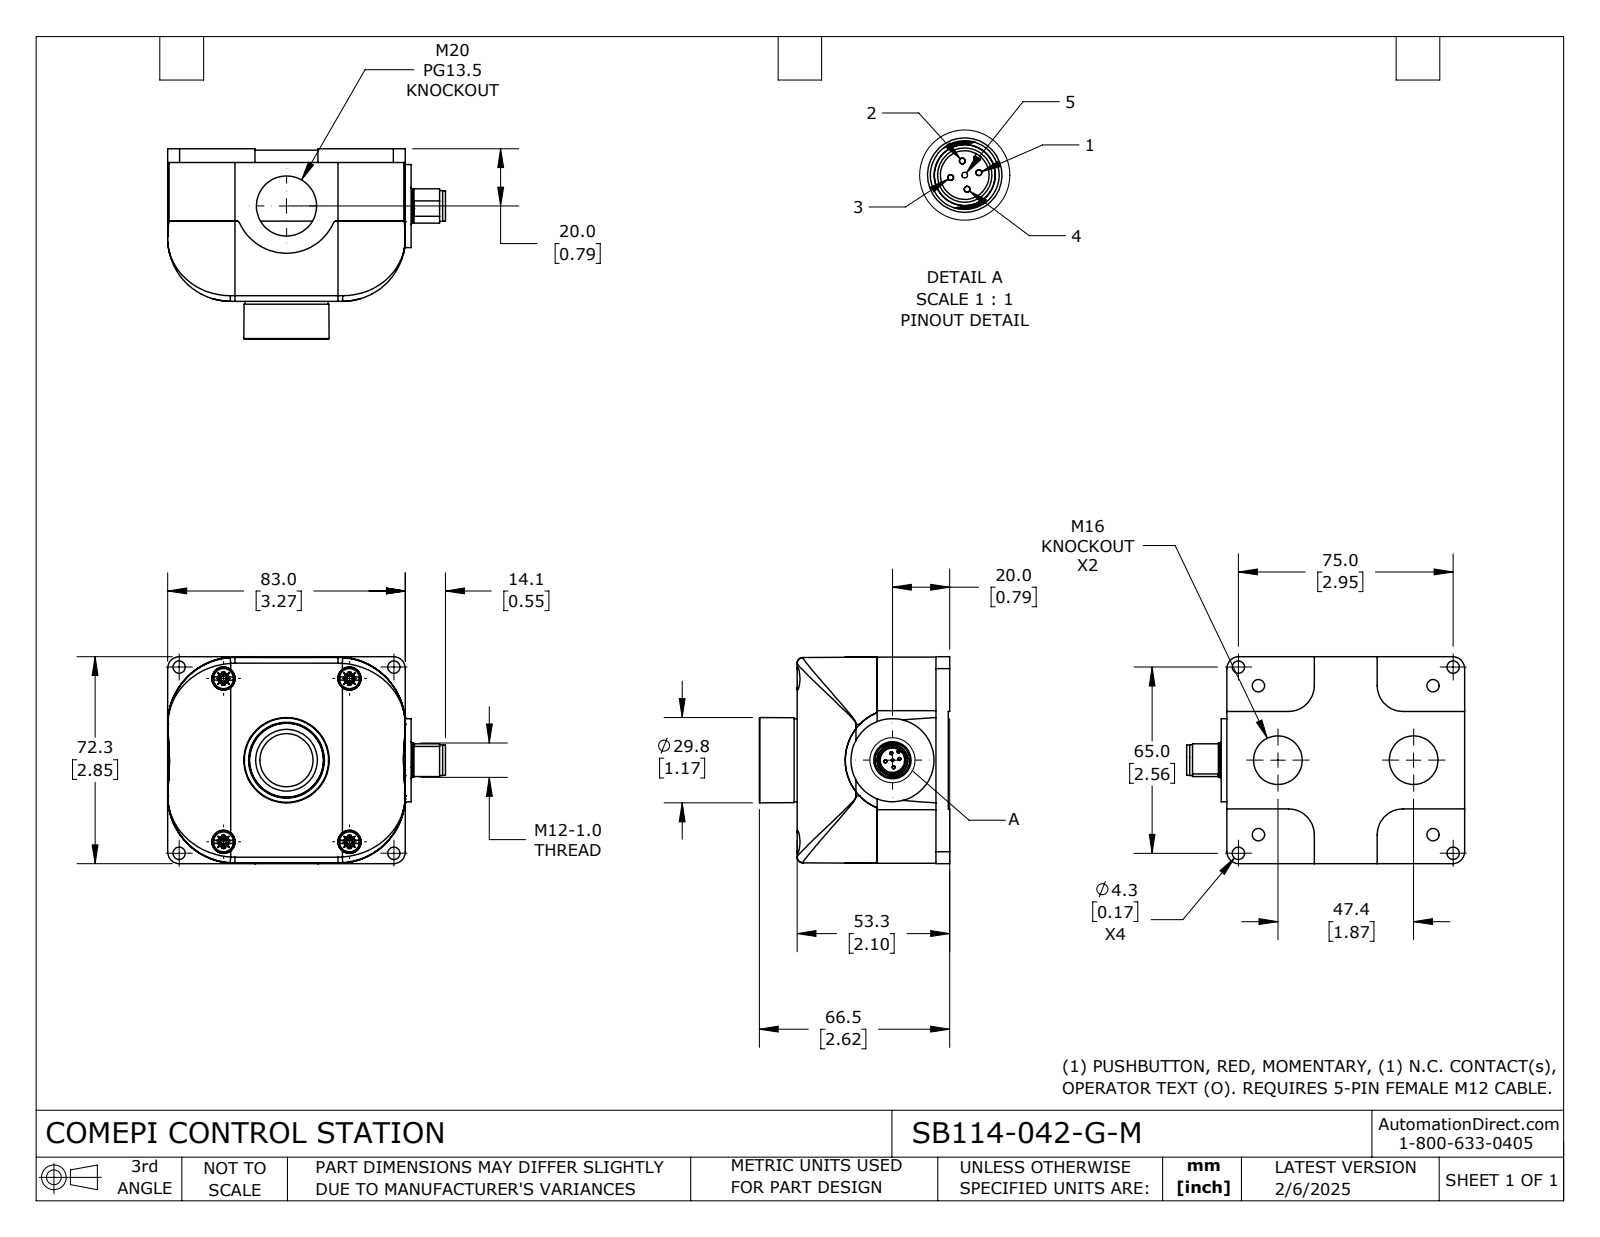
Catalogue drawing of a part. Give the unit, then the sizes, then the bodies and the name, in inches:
Units: inches
Overall size (bounding box): 3.821 × 2.846 × 2.618
Round holes (diameter × count): ⌀0.169 ×8, ⌀0.04 ×4, ⌀0.067 ×4, ⌀0.087 ×4, ⌀0.323 ×4, ⌀0.669 ×2, ⌀0.827 ×2, ⌀0.335 ×1, ⌀0.531 ×1, ⌀0.713 ×1, ⌀0.854 ×1
Round bosses / shafts (diameter × count): ⌀0.039 ×5, ⌀0.276 ×4, ⌀0.085 ×4, ⌀0.065 ×4, ⌀1.142 ×2, ⌀0.024 ×2, ⌀1.039 ×1, ⌀1.016 ×1
Partial cylindrical surfaces — rounded edges, fillets, slot ends (radius × count): R0.02 ×5, R0.035 ×4, R0.079 ×4, R0.354 ×4, R0.38 ×4, R0.925 ×4, R0.008 ×2, R0.01 ×2
Main face-to-face distances: 0.976, 0.098, 0.878, 2.079, 1.98, 1.102, 0.118, 2.098, 0.02, 0.996
Hole centre spacings: 0.376, 1.058, 1.39, 1.578, 1.954, 2.32, 2.367, 2.689
Volume: 13.23 in³ · Surface area: 95.33 in²
Bodies: 10 solids, 786 faces (370 planar, 273 cylindrical, 143 other)
Part name (STEP PRODUCT): SB114-042-G-M
STEP written by: SolidWorks 2024 (CONFIG_CONTROL_DESIGN)
